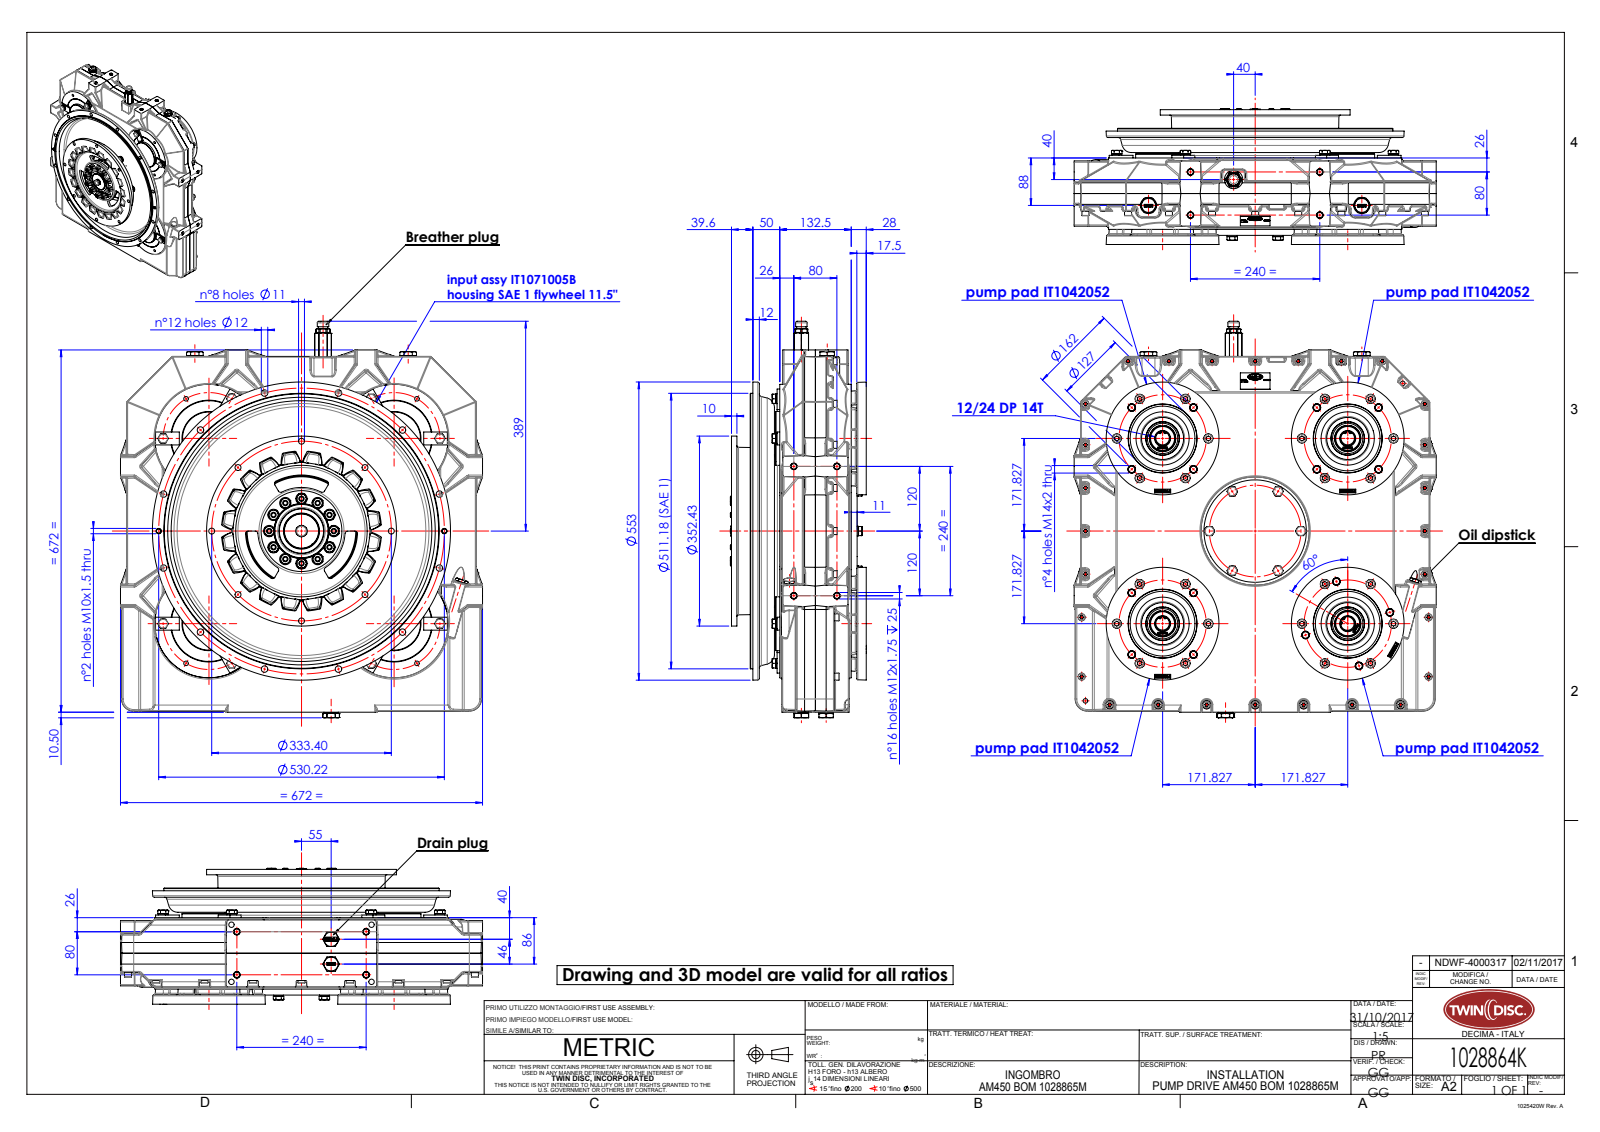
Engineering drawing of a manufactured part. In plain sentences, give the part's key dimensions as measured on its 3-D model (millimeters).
The part is named "ITam450-006_rev00-installation; IT4588040_rev00-installation; 1028864K; IT1042052_rev00-installation (+7 more)". Its 3-D file was written by "SolidWorks 2015 (AUTOMOTIVE_DESIGN)". It is 70 solids with 10368 faces: 4553 planar, 2730 cylindrical and 3085 other. Overall it measures 735.8 by 672.41 by 252.2 millimeters. Its volume is 10 380 000 cubic millimeters and its surface area 5 186 000 square millimeters. Round holes: 70 of diameter 8.5, 37 of diameter 12, 30 of diameter 11, 29 of diameter 10.2, 24 of diameter 17, 17 of diameter 14, 12 of diameter 10, 12 of diameter 10.5, 8 of diameter 2, 7 of diameter 12.2, 7 of diameter 13, 7 of diameter 16. Round bosses or shafts: 44 of diameter 10, 28 of diameter 13, 28 of diameter 8, 27 of diameter 16.2, 24 of diameter 16, 14 of diameter 18.1, 12 of diameter 21, 7 of diameter 21.1. Partial cylindrical surfaces (rounded edges, fillets, slot ends): 364 of radius 2.5, 106 of radius 2, 88 of radius 3, 84 of radius 1, 80 of radius 4, 58 of radius 0.45, 40 of radius 42.91, 36 of radius 5. The main face-to-face distances are 128.5, 4, 10, 148.5, 62.5, 66, 66.5, 28, 20, 86. The hole center spacings are 85, 120, 178.39, 243, 254.31, 57.4, 75, 106.89.
